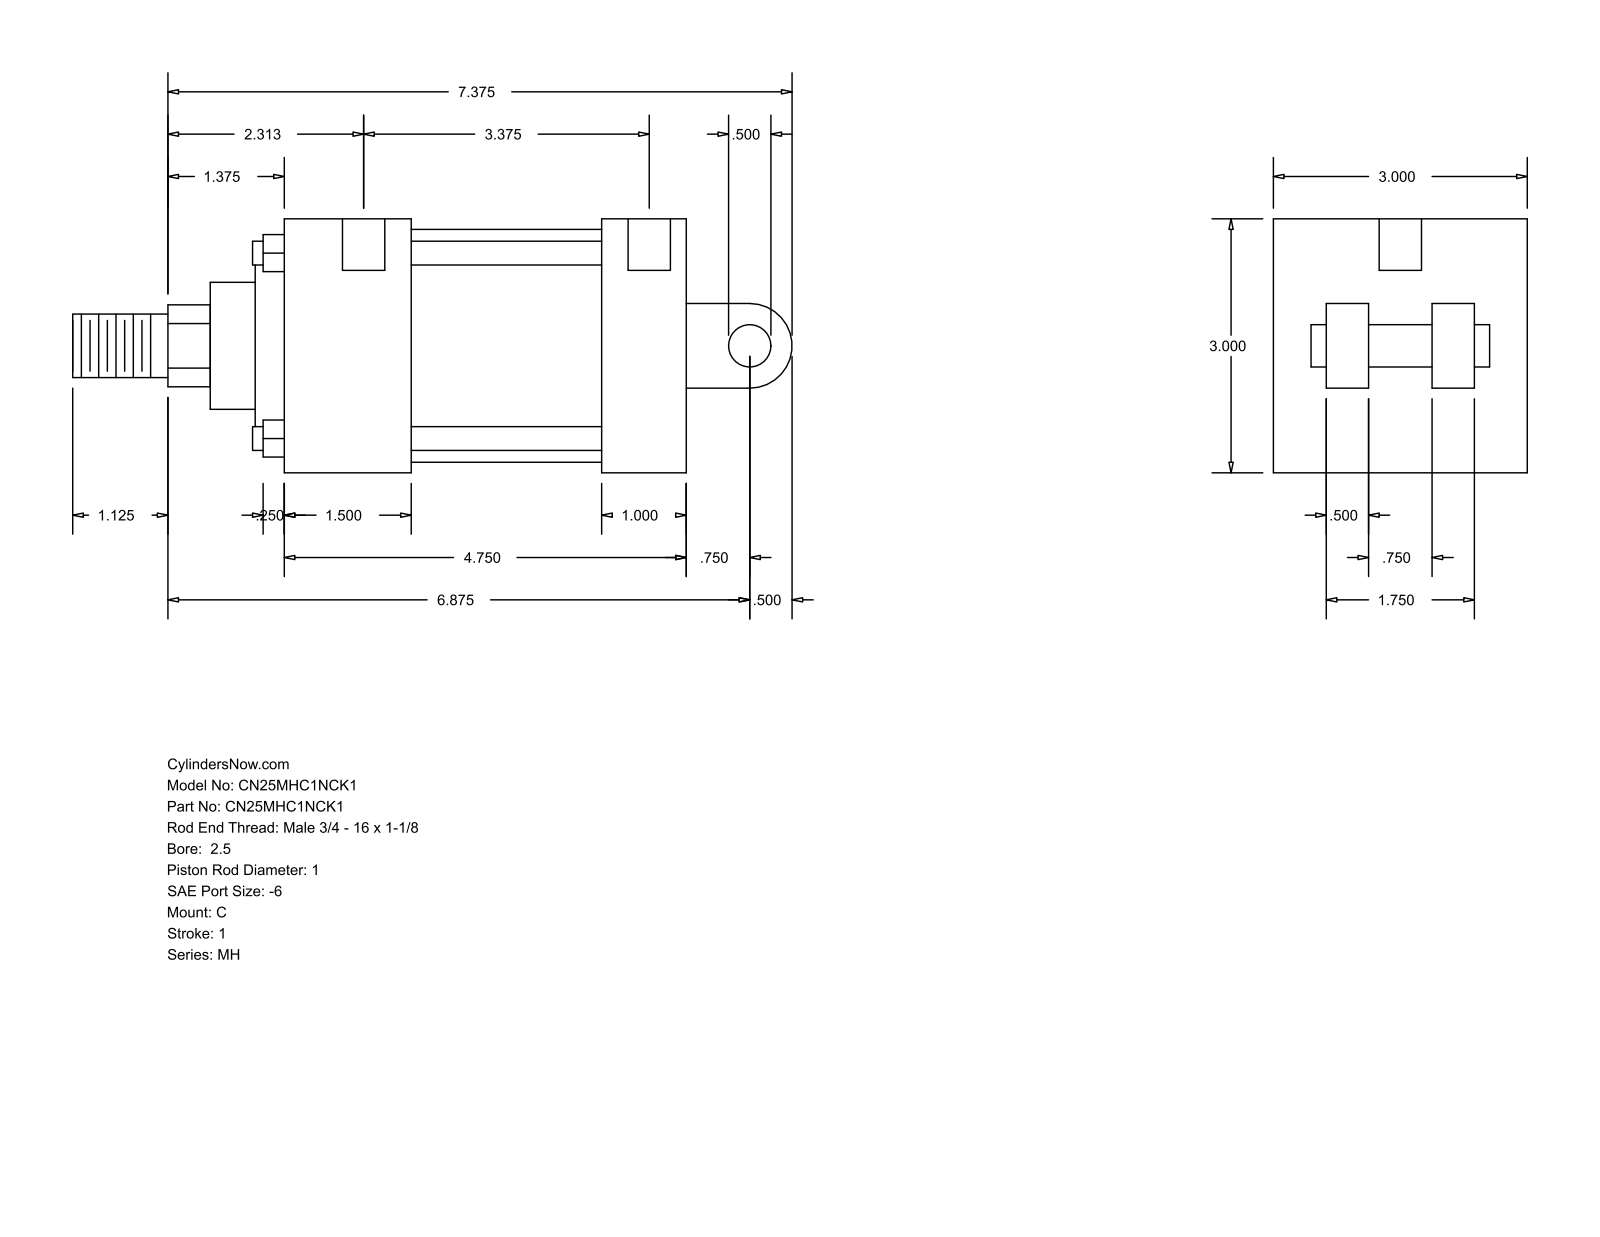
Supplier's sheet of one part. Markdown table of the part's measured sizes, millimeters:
| quantity | value |
| --- | --- |
| part name | MH_C__0250_1 |
| STEP written by | GSSL Pune (CONFIG_CONTROL_DESIGN) |
| units | millimeters |
| bodies | 0 solids, 101 faces (71 planar, 30 cylindrical, 0 other) |
| overall size | 215.9 × 76.2 × 76.2 |
| round holes (diameter × count) | 5.56 × 4, 12.7 × 2 |
| round bosses / shafts (diameter × count) | 7.14 × 4, 69.85 × 1, 60.33 × 1, 38.1 × 1, 25.4 × 1, 19.05 × 1, 12.7 × 1 |
| partial cylindrical surfaces (radius × count) | 12.29 × 1, 12.7 × 1 |
| main face-to-face distances | 76.2, 120.65, 25.39, 60.33, 15.87, 95.26, 38.11, 57.15, 82.54, 12.7 |
| hole center spacings | 93.66, 3.18, 4.76, 85.72, 88.9, 90.48 |
